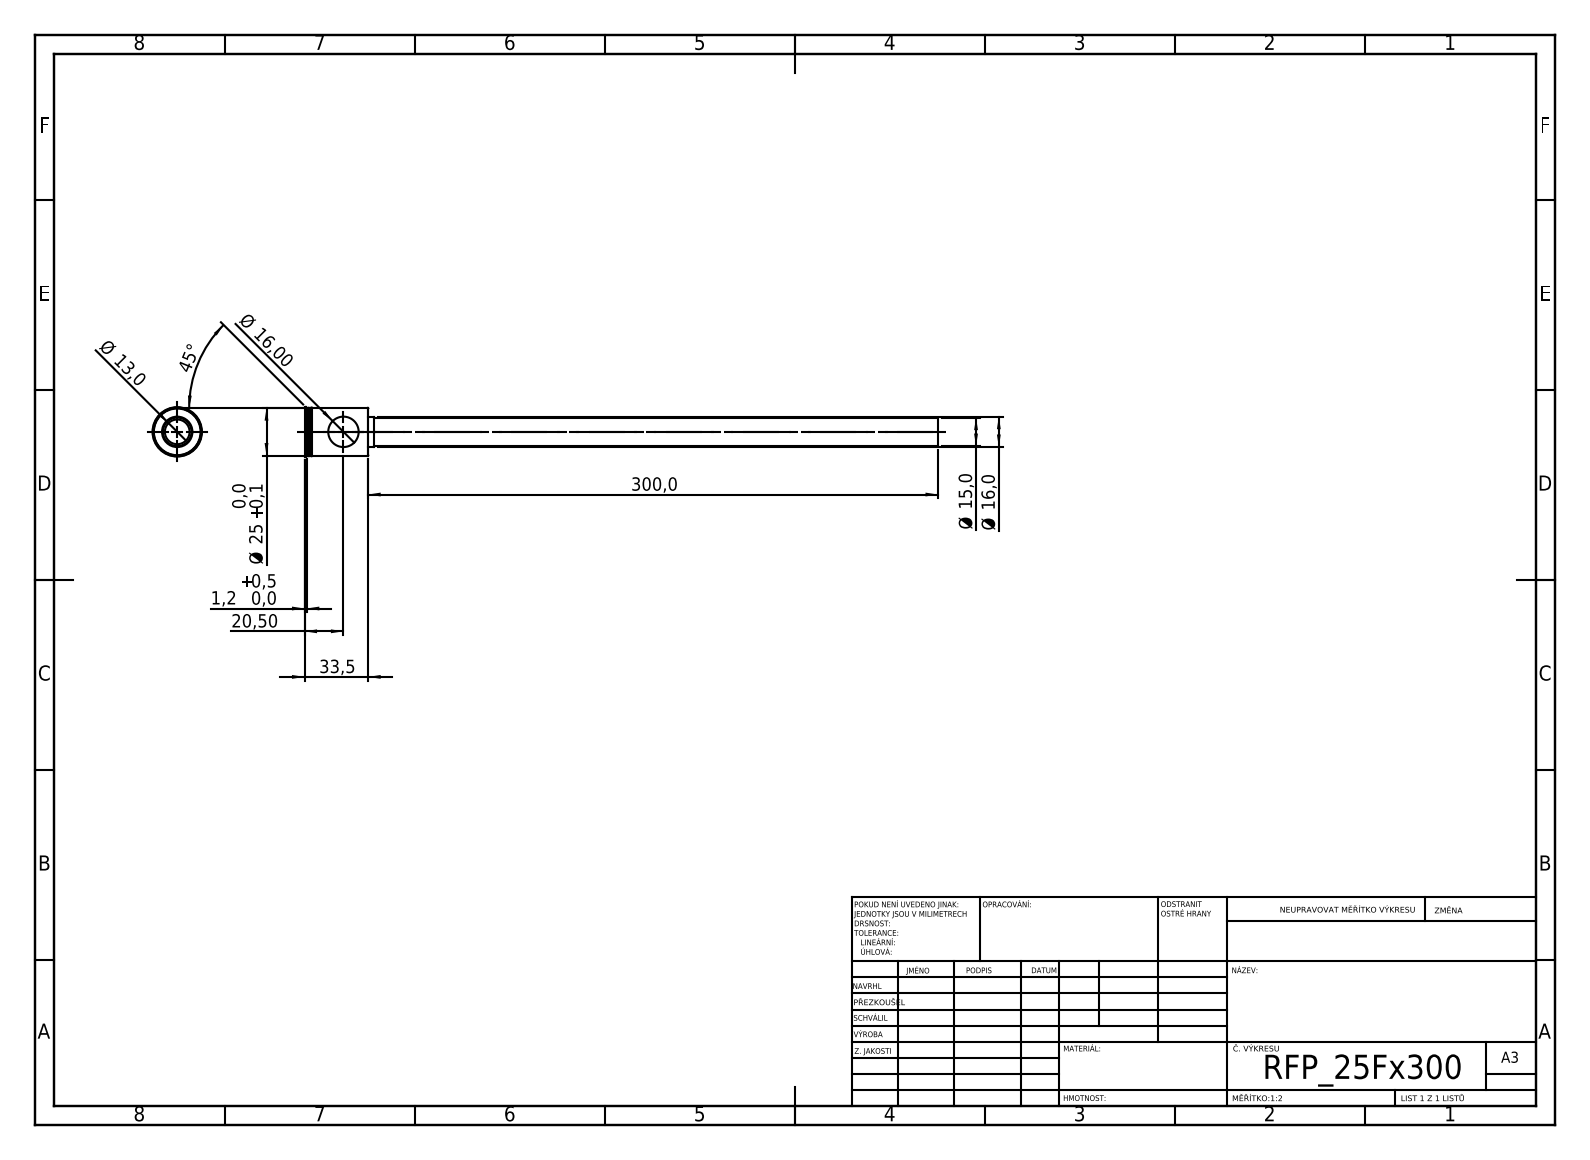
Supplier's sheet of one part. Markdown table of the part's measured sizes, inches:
| quantity | value |
| --- | --- |
| STEP written by | SolidWorks 2019 (CONFIG_CONTROL_DESIGN) |
| units | inches |
| bodies | 1 solid, 44 faces (20 planar, 16 cylindrical, 8 other) |
| overall size | 13.13 × 1.024 × 1.024 |
| volume | 1.435 in³ |
| surface area | 47.95 in² |
| round holes (diameter × count) | 0.512 × 1, 0.63 × 1 |
| round bosses / shafts (diameter × count) | 1.024 × 1, 0.984 × 1, 0.63 × 1, 0.591 × 1 |
| main face-to-face distances | 1.24, 0.079, 1.319, 0.803, 11.811, 13.051, 13.13, 0.02, 11.693, 0.118 |
